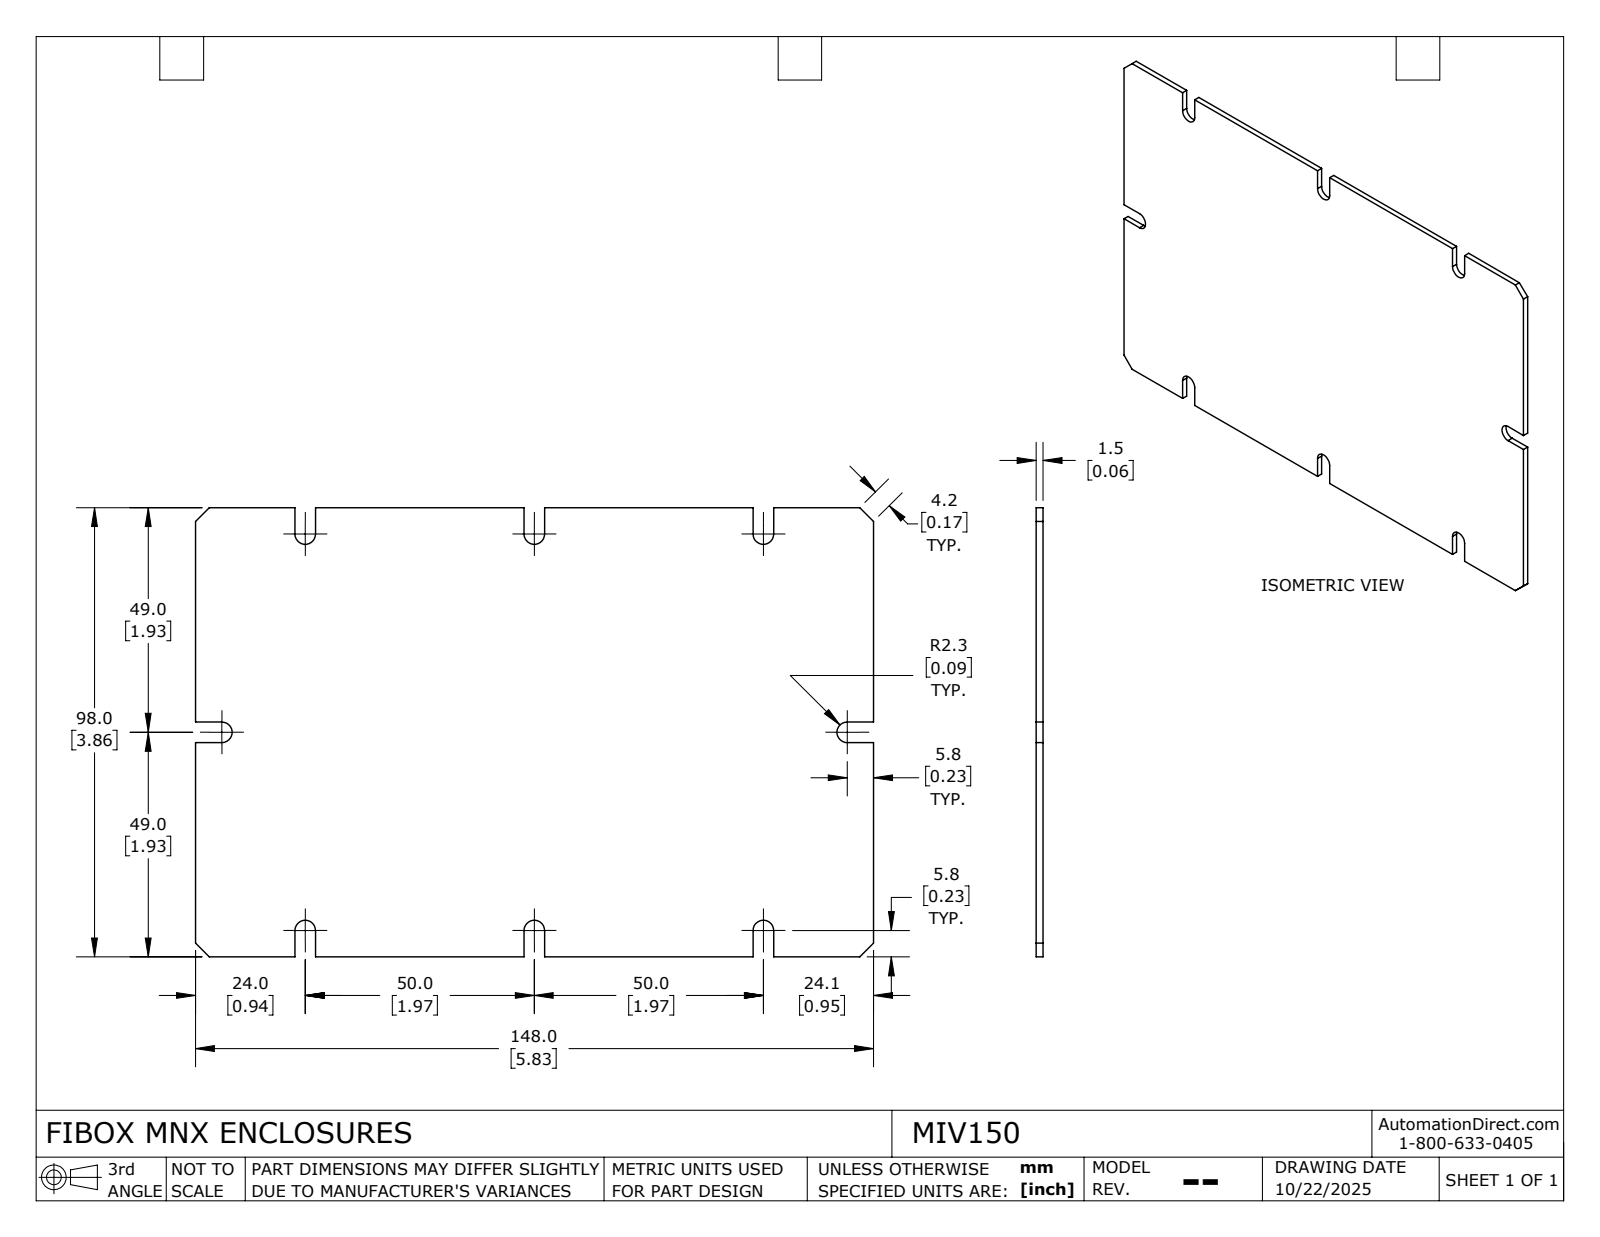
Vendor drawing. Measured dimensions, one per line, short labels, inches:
name: MIV150_Default
written by: SolidWorks 2024 (CONFIG_CONTROL_DESIGN)
unit: in
bodies: 1 solid, 42 faces (34 planar, 8 cylindrical, 0 other)
size: 5.827 × 3.858 × 0.059
volume: 1.301 in³; area: 45.46 in²
rounds: 8× R0.089
face distances: 0.059, 3.858, 5.827, 0.177, 1.969, 1.841, 2.018, 3.937, 2.146, 1.791
